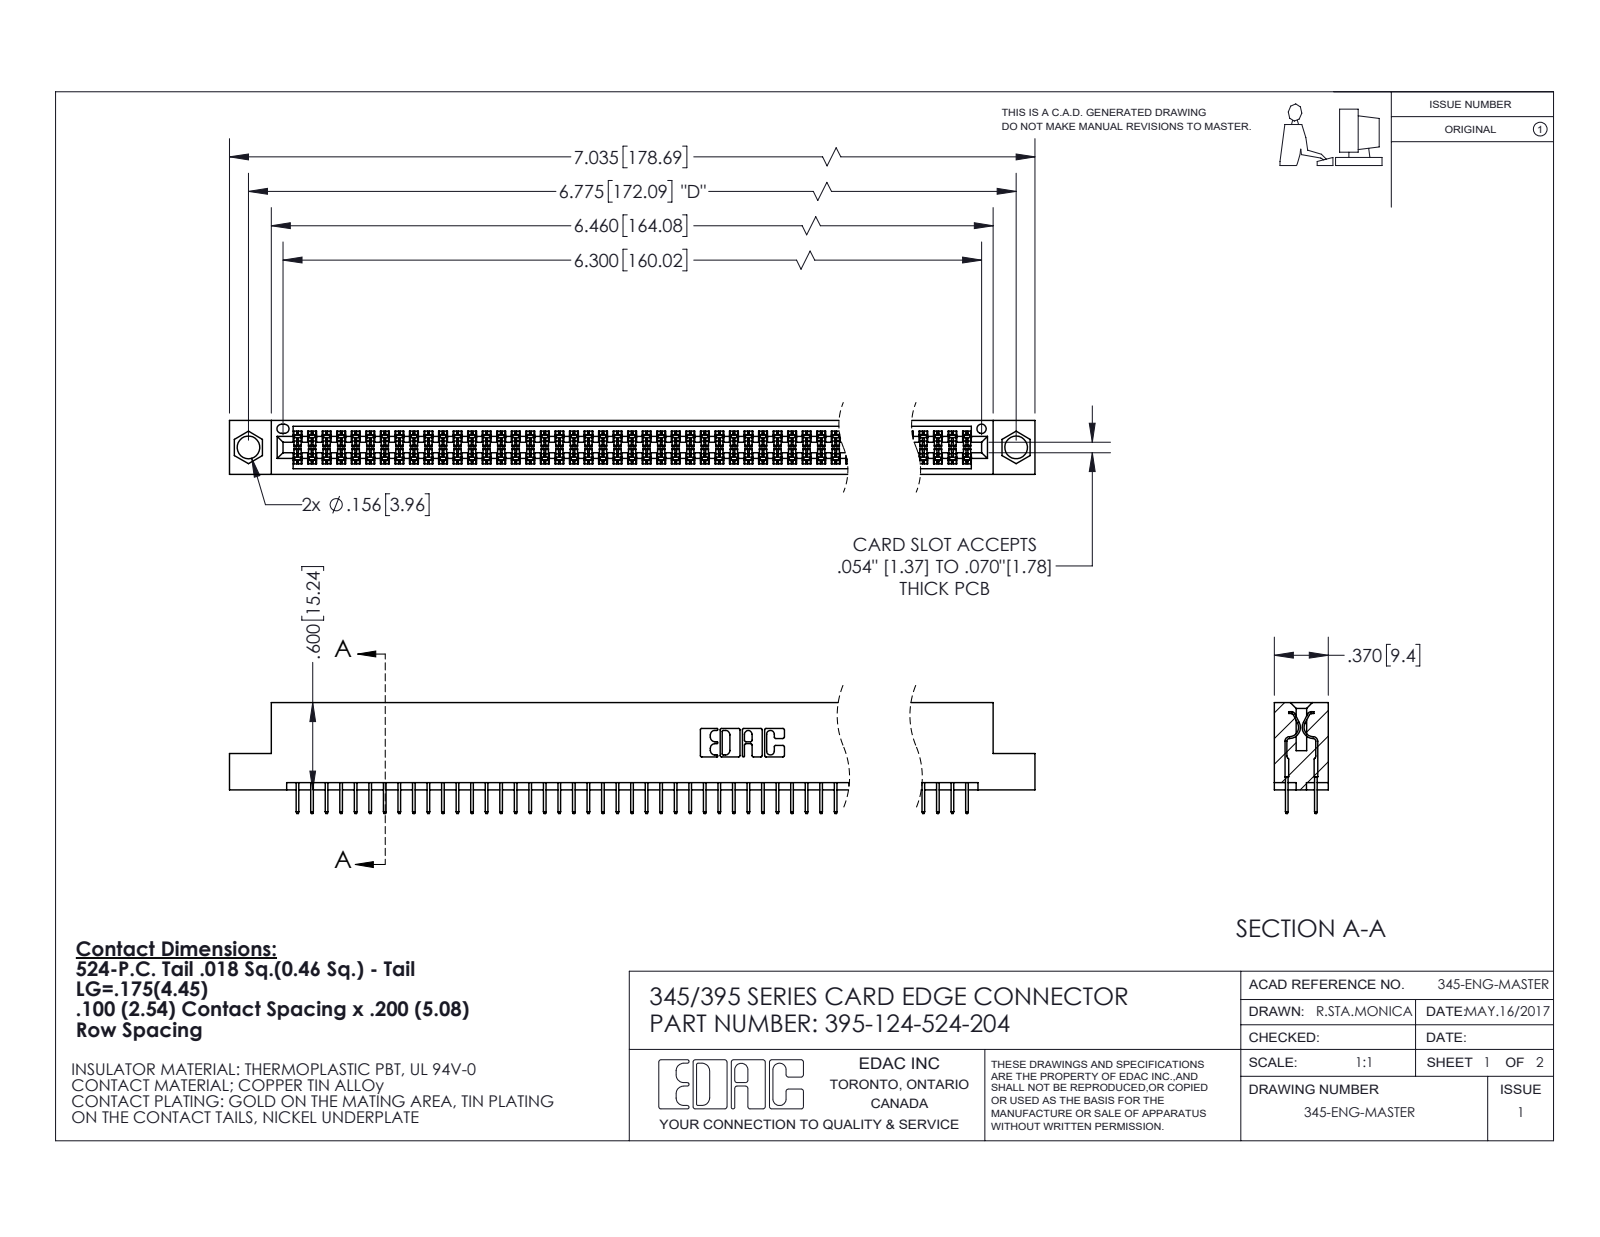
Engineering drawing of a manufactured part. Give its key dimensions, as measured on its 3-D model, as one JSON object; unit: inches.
{"part_name": "395-124-524-204; 345-292-001_345-293-124; 345 Part_Flush Mounting Lugs - 0.156 Dia-TI", "step_written_by": "SolidWorks 2020 (CONFIG_CONTROL_DESIGN)", "units": "inches", "bodies": {"solids": 125, "faces": 6836, "planar": 4930, "cylindrical": 1906, "other": 0}, "overall_size": [7.035, 0.762, 0.37], "volume_in3": 1.053, "surface_area_in2": 39.13, "round_holes": [[0.156, 2], [0.064, 1]], "partial_cylinders_radius": [[0.006, 187], [0.01, 22], [0.007, 6], [0.031, 6], [0.026, 3], [0.014, 2], [0.019, 2], [0.022, 2]], "face_to_face_distances": [0.072, 0.298, 0.2, 0.37, 0.098, 0.272, 0.025, 0.225, 0.072, 0.175], "hole_center_spacings": [0.27, 6.539, 6.775]}
